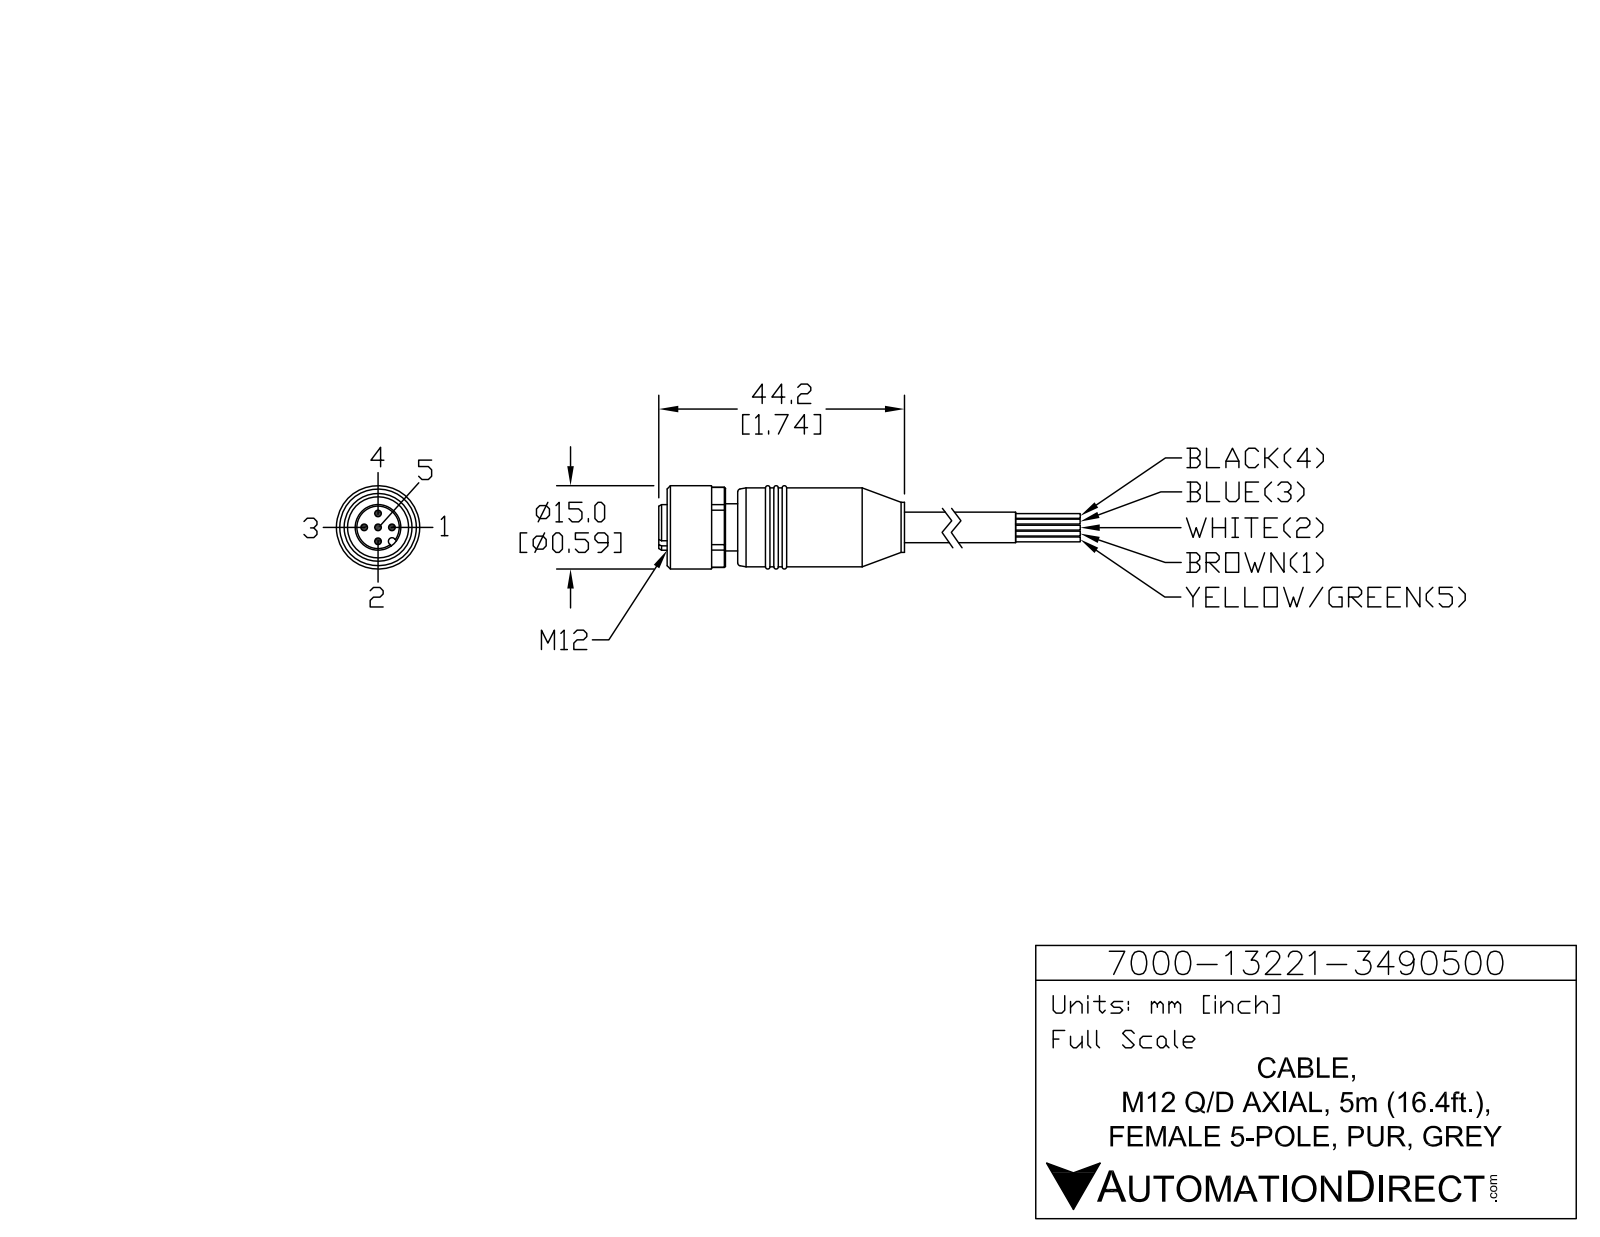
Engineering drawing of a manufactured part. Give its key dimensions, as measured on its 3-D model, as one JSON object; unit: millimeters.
{"part_name": "7000-13221-3490500", "step_written_by": "SolidWorks 2015 (AUTOMOTIVE_DESIGN)", "units": "millimeters", "bodies": {"solids": 1, "faces": 94, "planar": 28, "cylindrical": 38, "other": 28}, "overall_size": [64.2, 15, 15], "volume_mm3": 6622, "surface_area_mm2": 3349, "round_holes": [[1.2, 5], [11, 1]], "round_bosses_or_shafts": [[15, 1], [14.2, 1], [9, 1], [8.5, 1], [8.2, 1], [6.5, 1]], "partial_cylinders_radius": [[0.65, 1], [7.2, 1]], "face_to_face_distances": [2.2, 13, 3, 5.2, 9, 12, 14.2, 64.2, 55.2, 52.2], "hole_center_spacings": [2.5, 3.54, 5]}
